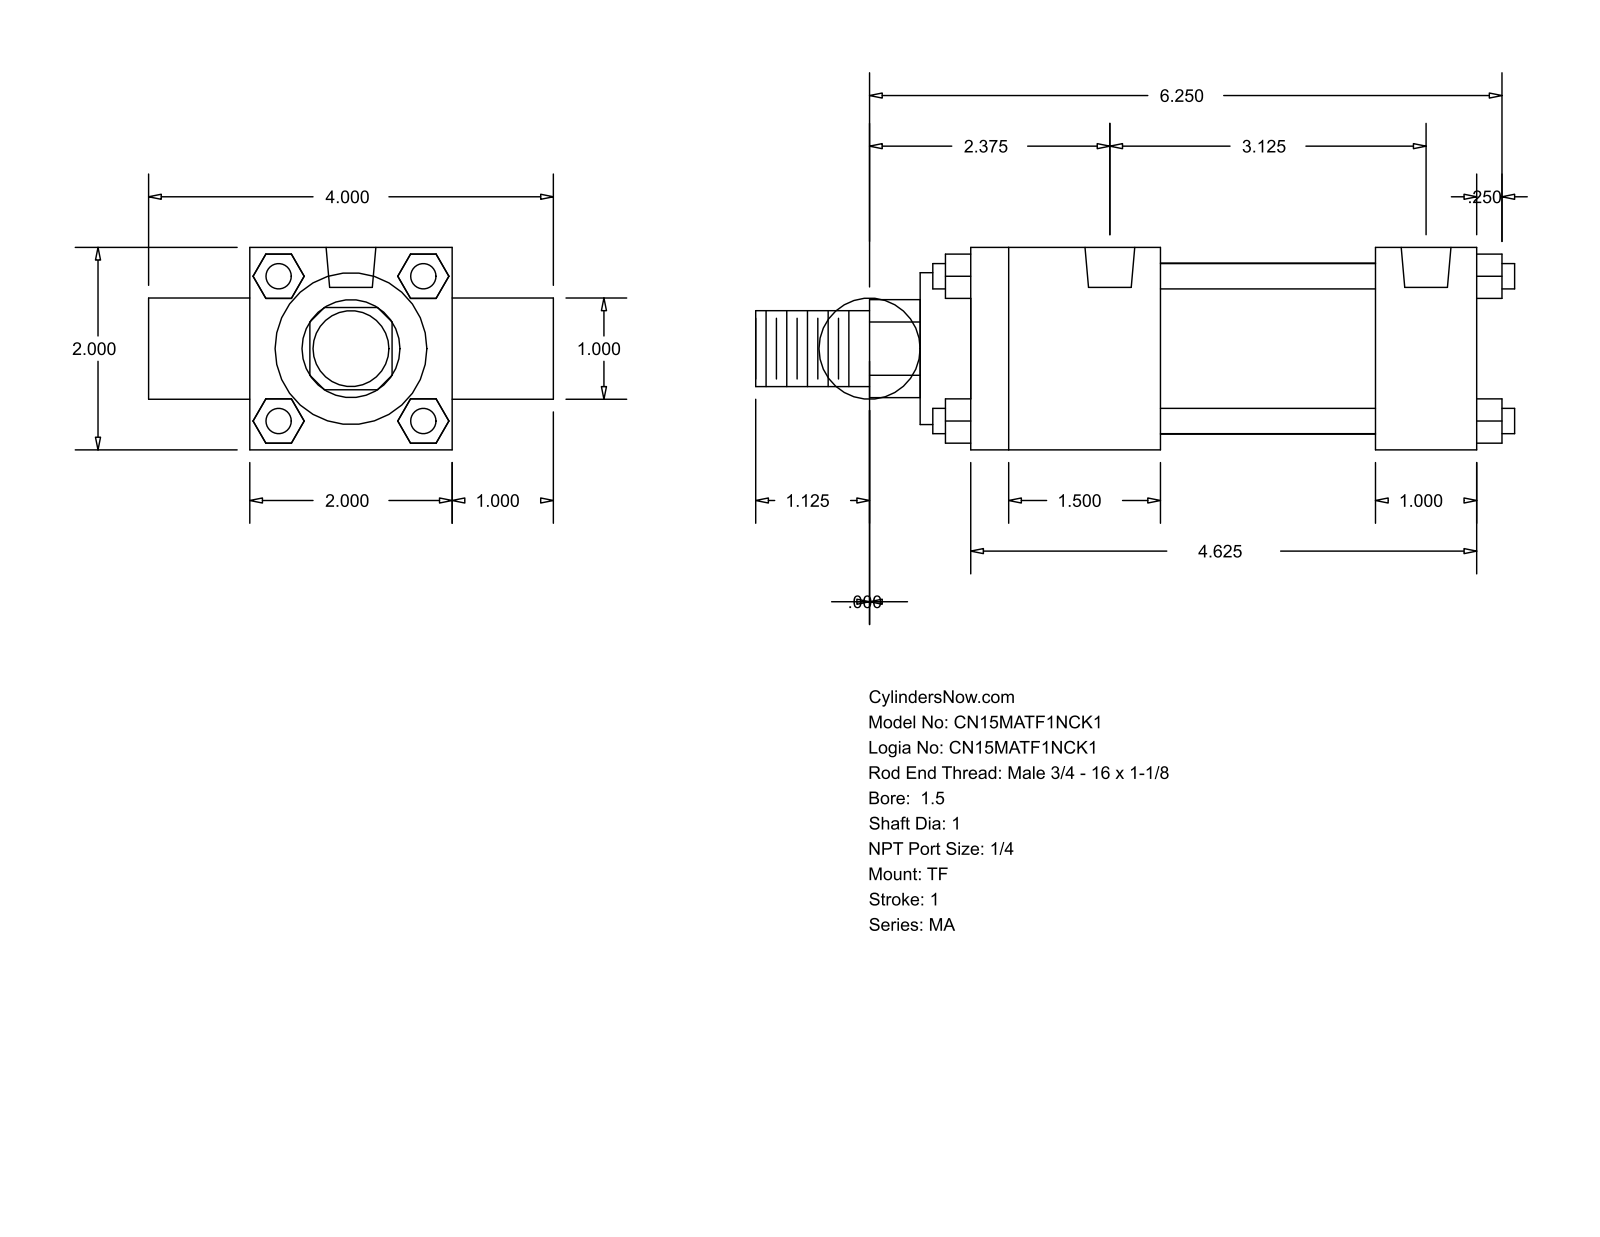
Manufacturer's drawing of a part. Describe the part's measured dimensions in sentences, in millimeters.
The part is named "MA_TF__0150_1". Its 3-D file was written by "GSSL Pune (CONFIG_CONTROL_DESIGN)". It is 0 solids with 120 faces: 92 planar, 28 cylindrical and 0 other. Overall it measures 190.5 by 101.6 by 50.8 millimeters. Round holes: 3 of diameter 7.94, 2 of diameter 12.49. Round bosses or shafts: 4 of diameter 6.35, 2 of diameter 25.4, 1 of diameter 42.93, 1 of diameter 38.1, 1 of diameter 19.05. Partial cylindrical surfaces (rounded edges, fillets, slot ends): 1 of radius 12.29. The main face-to-face distances are 50.8, 25.4, 101.6, 53.97, 127, 76.2, 6.35, 47.63, 79.37, 139.7. The hole center spacings are 79.37.
